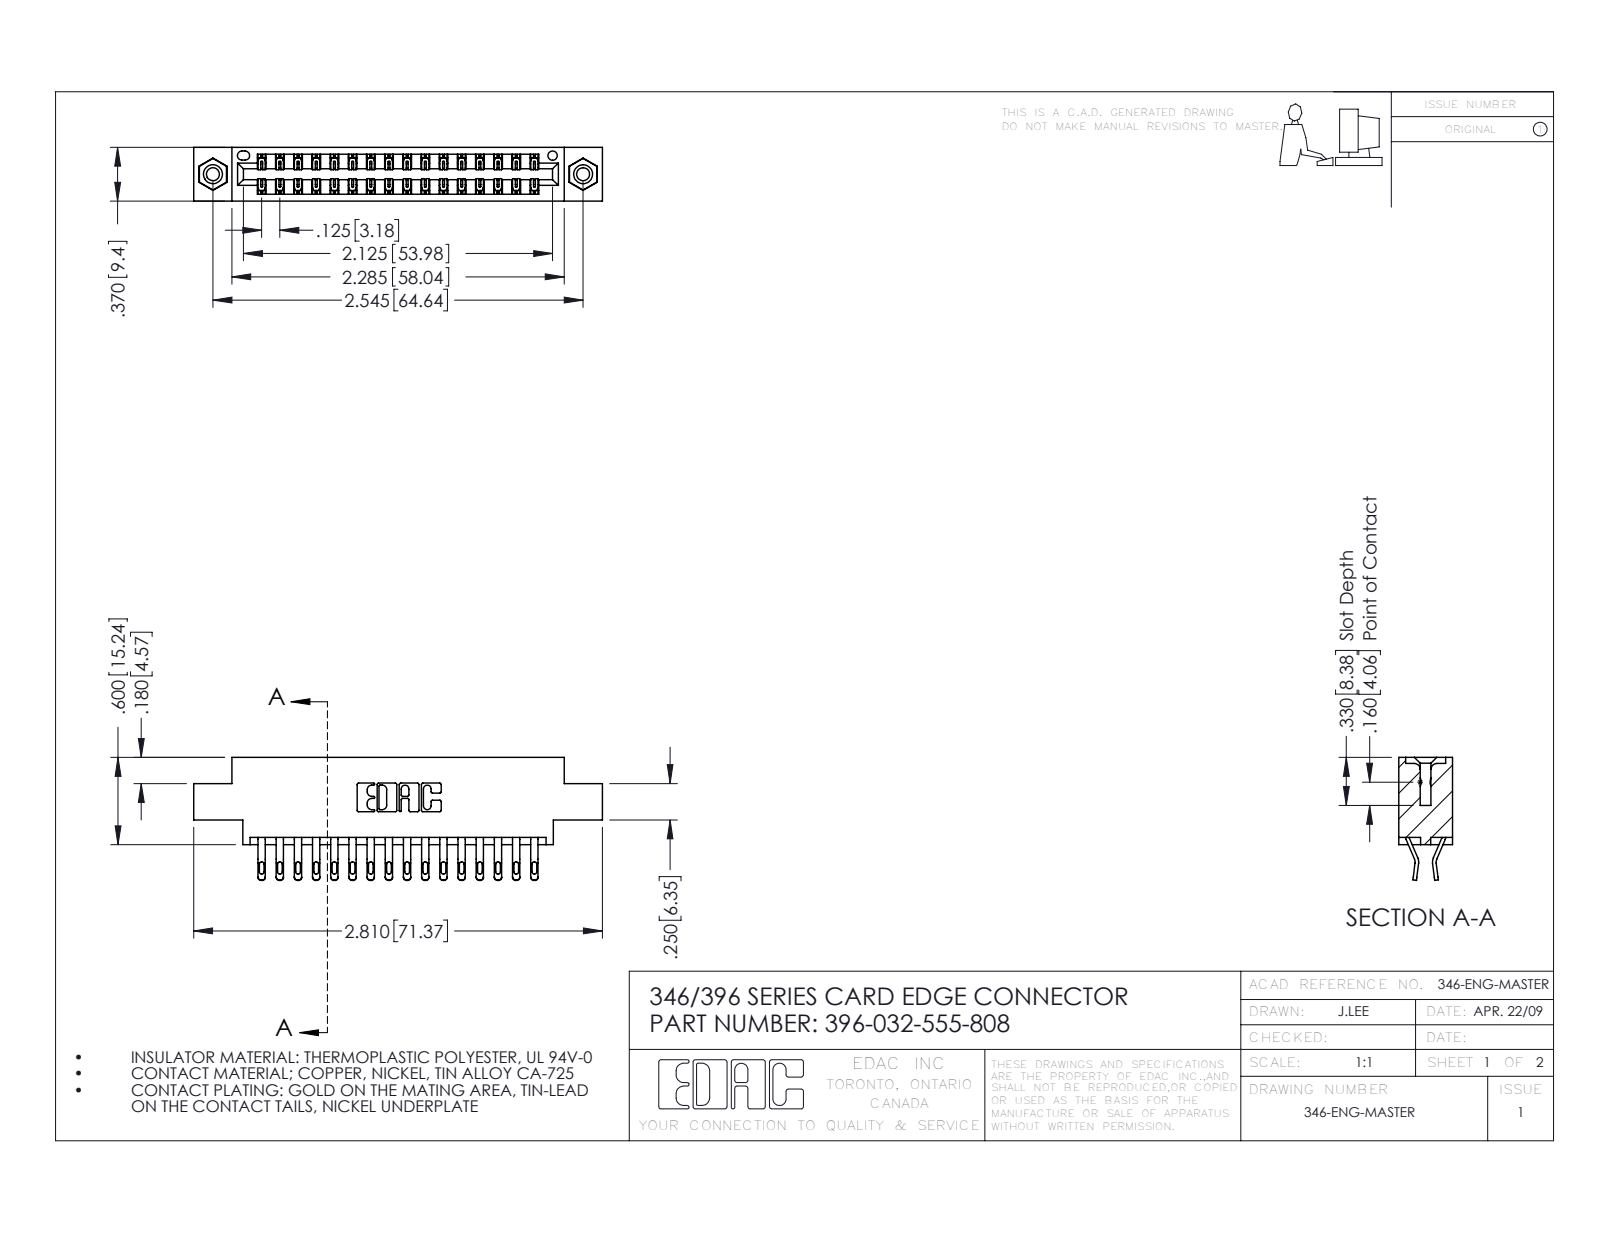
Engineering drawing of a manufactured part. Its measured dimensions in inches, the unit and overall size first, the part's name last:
Units: inches
Overall size (bounding box): 2.81 × 0.845 × 0.37
Round holes (diameter × count): ⌀0.089 ×2, ⌀0.125 ×2, ⌀0.156 ×2, ⌀0.064 ×1
Round bosses / shafts (diameter × count): ⌀0.155 ×2
Partial cylindrical surfaces — rounded edges, fillets, slot ends (radius × count): R0.016 ×64, R0.02 ×64, R0.006 ×48, R0.01 ×22, R0.007 ×6, R0.031 ×6, R0.026 ×3, R0.01 ×2
Main face-to-face distances: 0.048, 0.322, 0.37, 0.25, 0.025, 0.072, 0.298, 0.275, 0.222, 0.148
Hole centre spacings: 0.246, 2.338, 2.545
Volume: 0.408 in³ · Surface area: 14.44 in²
Bodies: 35 solids, 2042 faces (1168 planar, 858 cylindrical, 16 other)
Part name (STEP PRODUCT): 345-250-001_345-250-003-102; 346 Part_0.170 Offset - 0.156 Dia-TI; 396-032-555-808; 345-292-001_555 Tail
STEP written by: SolidWorks 2016 (CONFIG_CONTROL_DESIGN)
